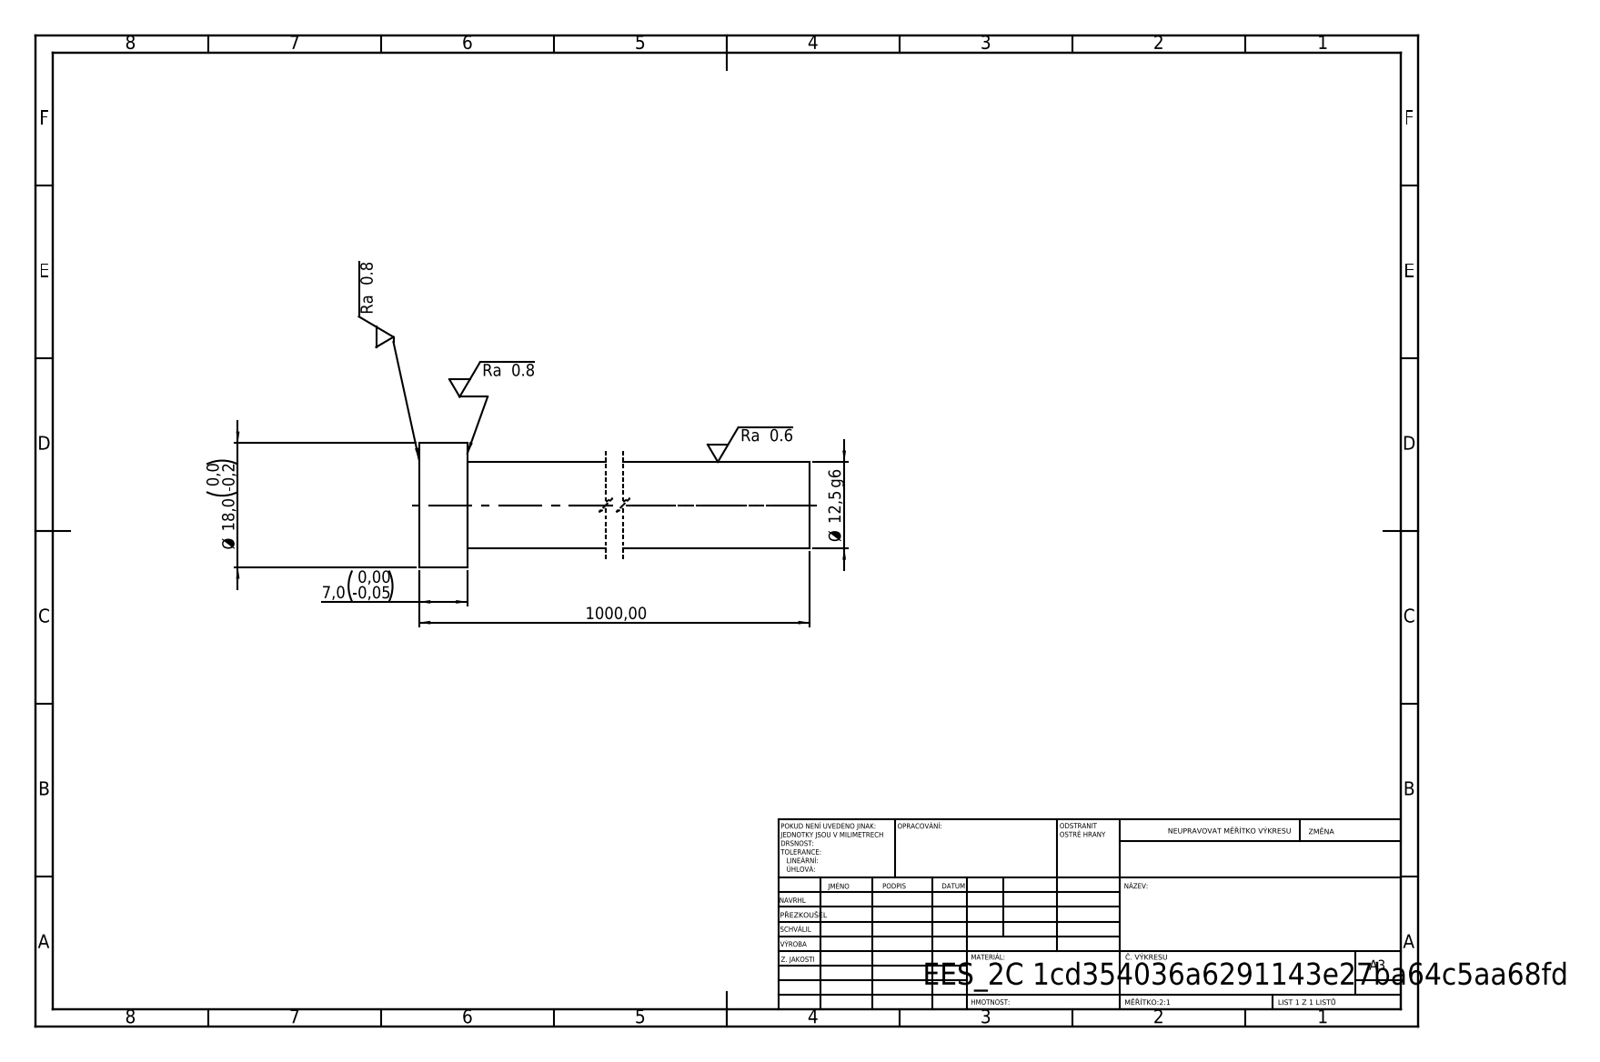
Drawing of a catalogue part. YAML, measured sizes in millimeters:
step_written_by: "SolidWorks 2019 (CONFIG_CONTROL_DESIGN)"
units: millimeters
bodies: {solids: 1, faces: 7, planar: 3, cylindrical: 4, other: 0}
overall_size: [1000, 18, 18]
volume: 123641
surface_area: 39900
round_bosses_or_shafts:
  - {diameter: 18, count: 1}
  - {diameter: 12.5, count: 1}
face_to_face_distances: [7, 1000, 993]
